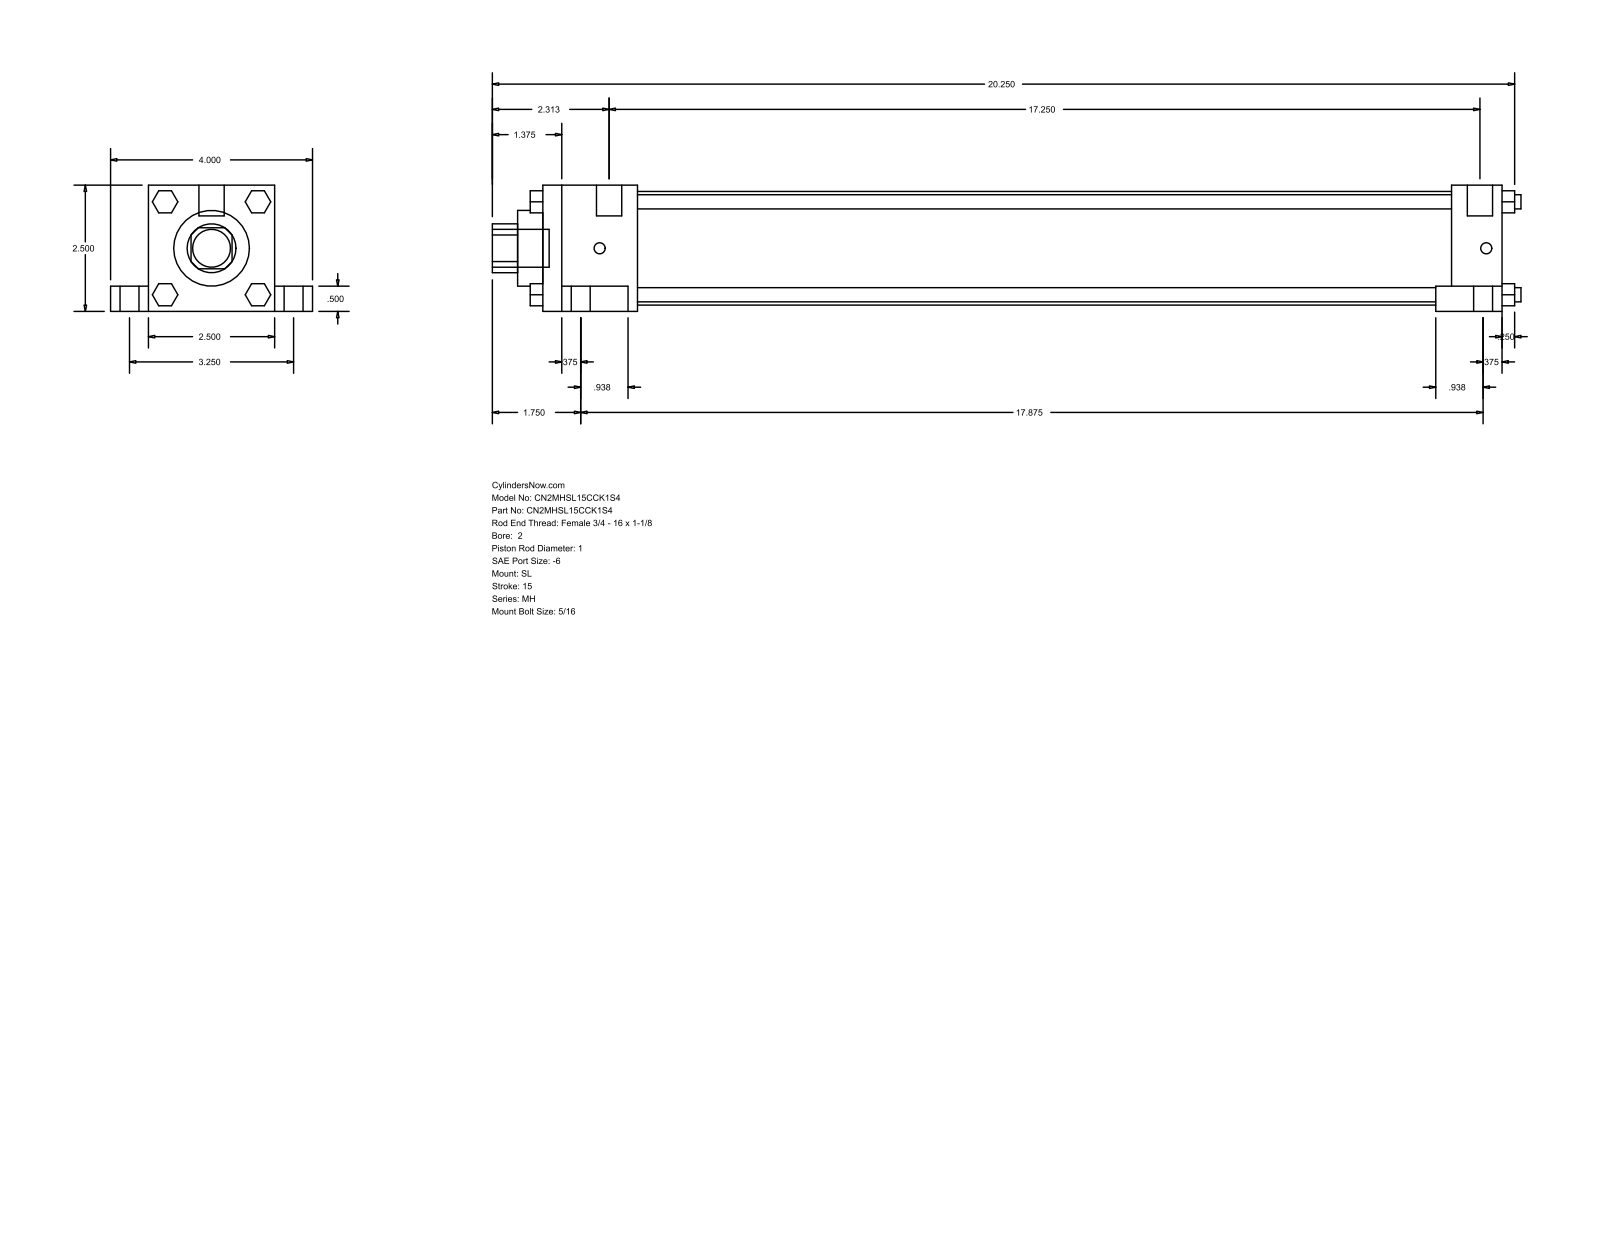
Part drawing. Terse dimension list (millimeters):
name: MH_SL__0200_1
written by: GSSL Pune (CONFIG_CONTROL_DESIGN)
unit: mm
bodies: 0 solids, 148 faces (112 planar, 36 cylindrical, 0 other)
size: 517.52 × 101.6 × 63.5
holes: 1× ⌀25.4, 1× ⌀38.1, 1× ⌀57.15
bosses: 4× ⌀15.88, 4× ⌀9.53, 4× ⌀7.14, 4× ⌀5.56, 2× ⌀12.7, 1× ⌀19.05
rounds: 1× R12.29
face distances: 63.5, 482.6, 12.7, 19.05, 50.8, 82.55, 9.52, 25.4, 457.2, 47.63
